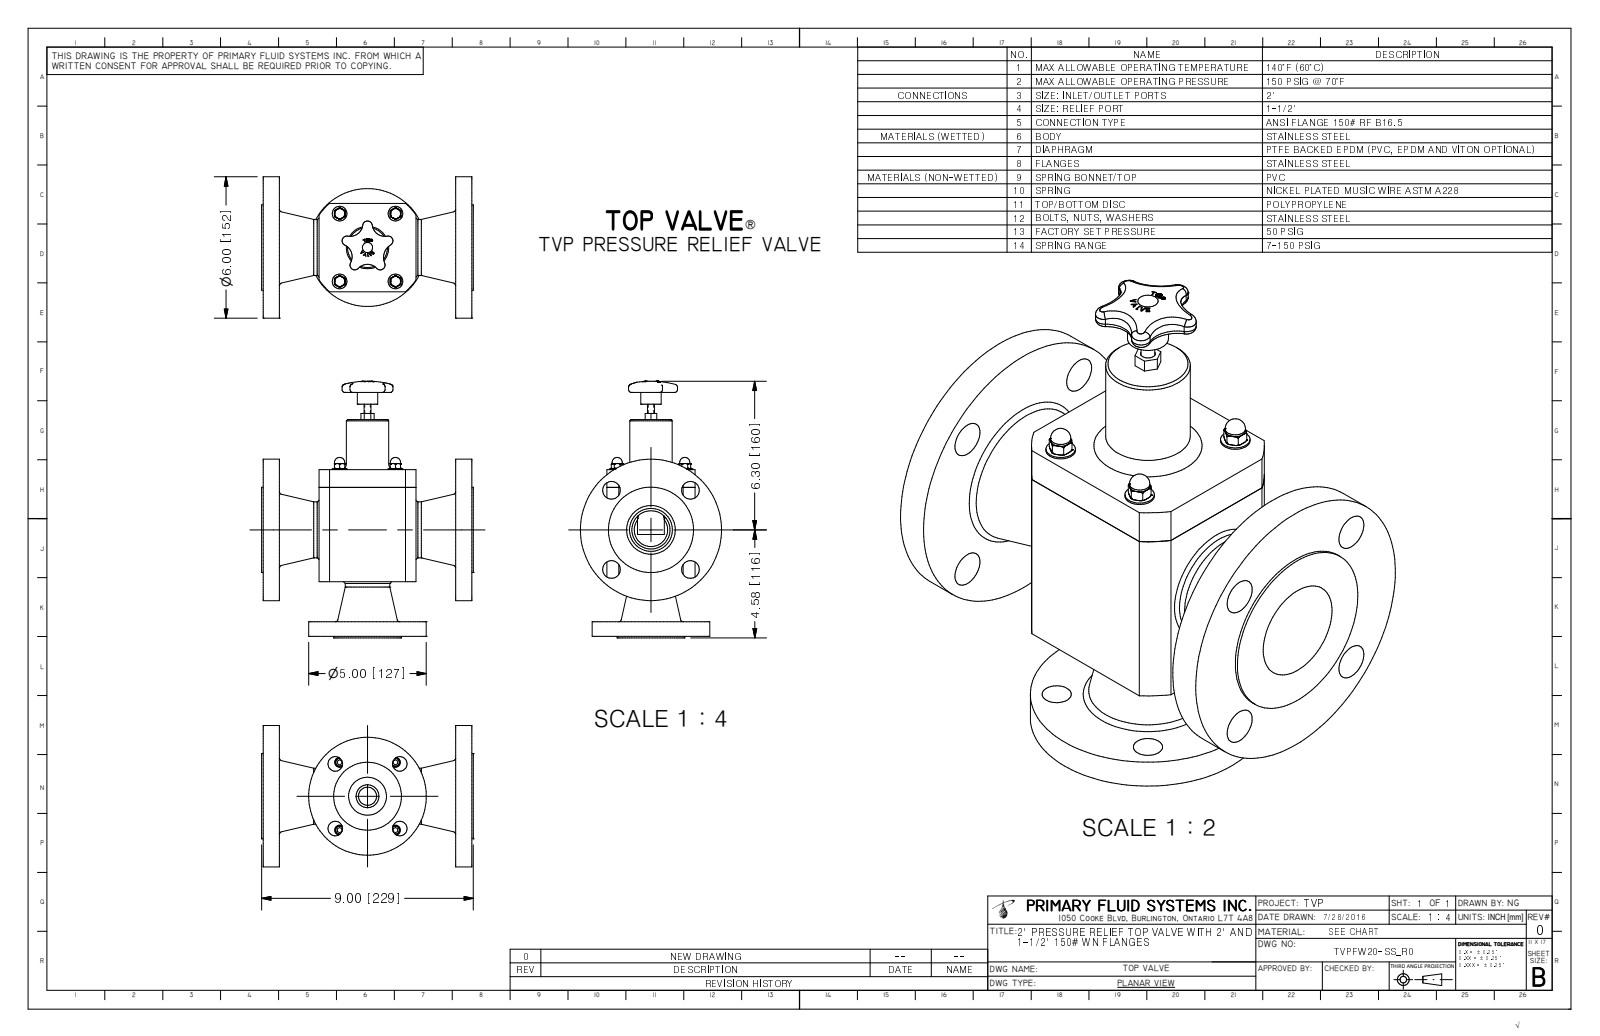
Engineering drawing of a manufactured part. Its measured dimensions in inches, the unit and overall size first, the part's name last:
Units: inches
Overall size (bounding box): 10.88 × 9 × 6
Round holes (diameter × count): ⌀0.175 ×4, ⌀0.62 ×4, ⌀0.75 ×4, ⌀1.61 ×1, ⌀2.067 ×1
Round bosses / shafts (diameter × count): ⌀0.625 ×4, ⌀0.433 ×4, ⌀0.375 ×4, ⌀6 ×1, ⌀5 ×1, ⌀3.62 ×1, ⌀2.88 ×1, ⌀2.375 ×1
Partial cylindrical surfaces — rounded edges, fillets, slot ends (radius × count): R0.085 ×5, R0.205 ×5, R0.536 ×4, R0.656 ×4, R0.625 ×1, R0.745 ×1, R2.475 ×1
Main face-to-face distances: 0.69, 8.185, 0.063, 7.495, 2.375, 8.875, 6.5, 1.685, 5.81, 3.75
Hole centre spacings: 1.94, 2.375, 2.56, 2.743, 3.359, 0.196, 0.196, 1.864
Volume: 130.1 in³ · Surface area: 383.7 in²
Bodies: 1 solid, 376 faces (154 planar, 67 cylindrical, 155 other)
Part name (STEP PRODUCT): TVPFW20-SS_R0
STEP written by: Autodesk Inventor 2009 (AUTOMOTIVE_DESIGN)
